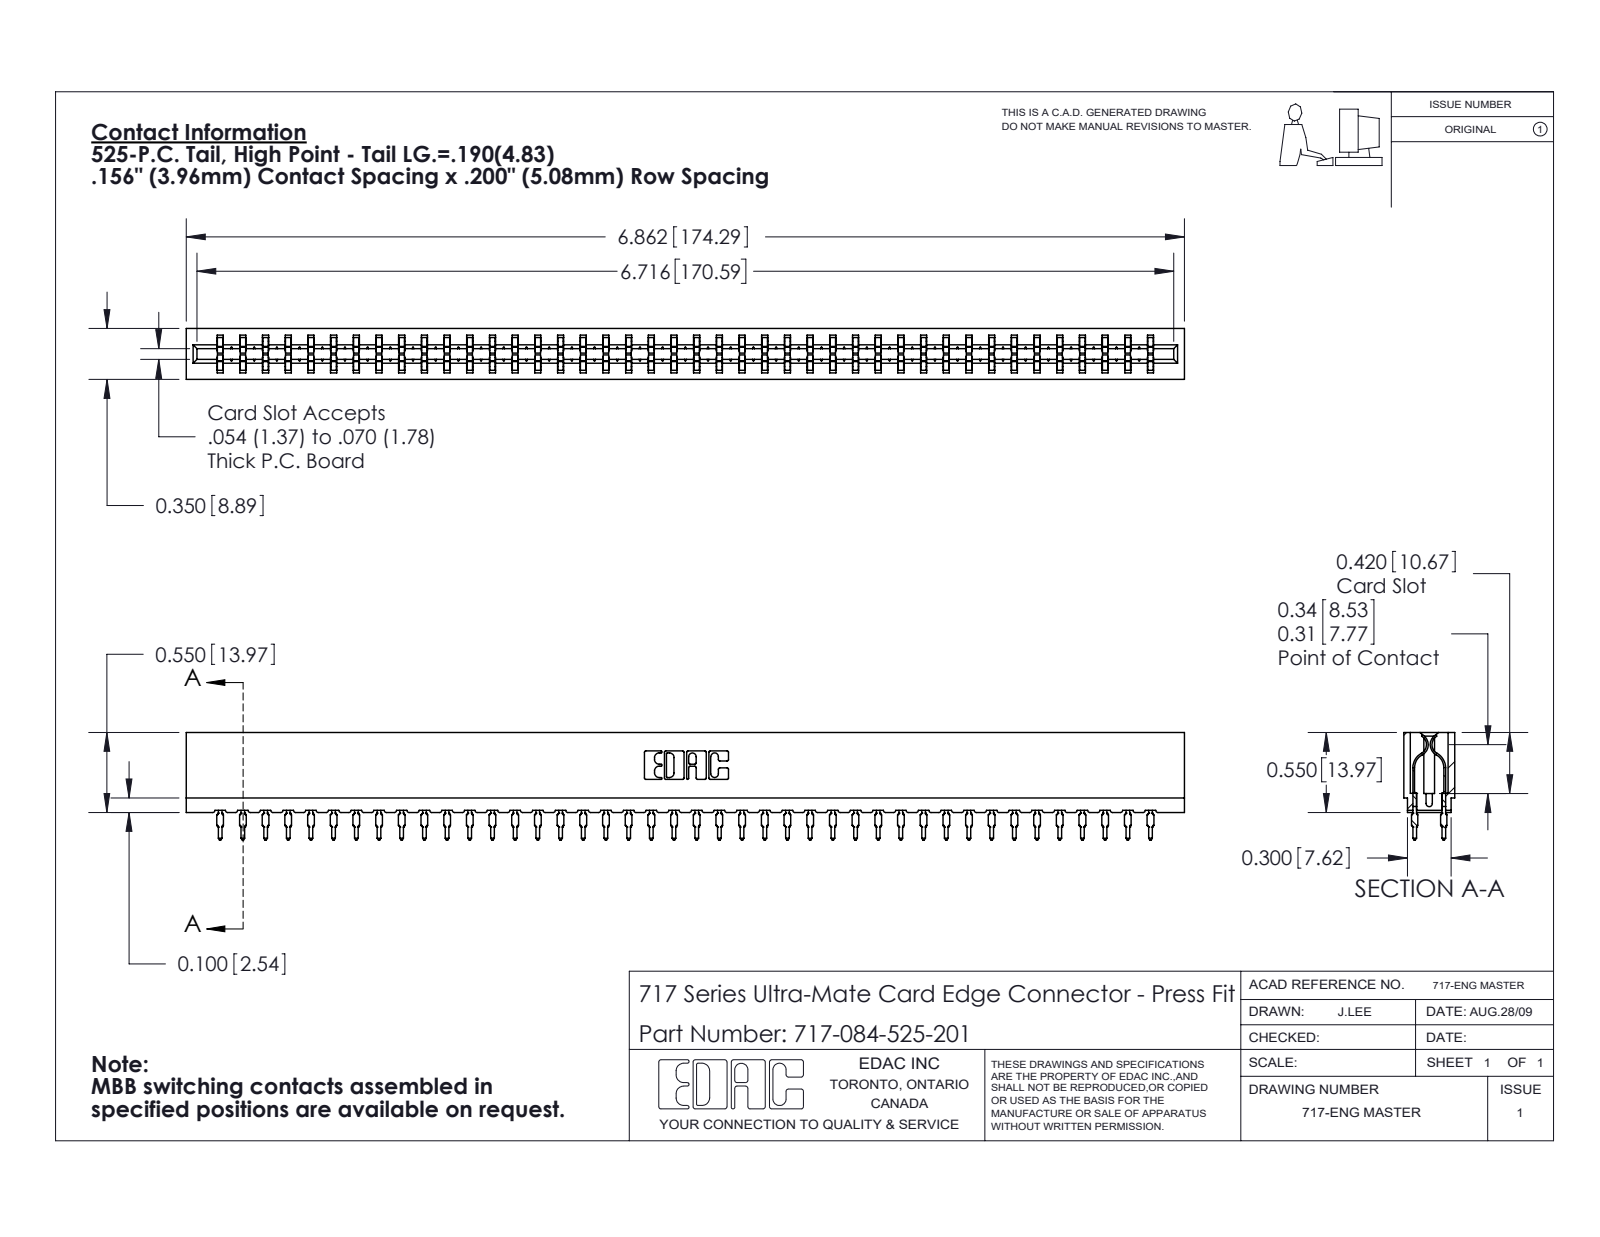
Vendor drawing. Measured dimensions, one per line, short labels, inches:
name: 717-084-525-201; 717 Part_Insulator Option - 06; 745-292-001_525
written by: SolidWorks 2020 (CONFIG_CONTROL_DESIGN)
unit: in
bodies: 85 solids, 7654 faces (3960 planar, 1510 cylindrical, 2184 other)
size: 6.862 × 0.739 × 0.35
volume: 0.92 in³; area: 35.61 in²
rounds: 168× R0.021, 84× R0.015, 22× R0.01, 8× R0.005, 8× R0.011, 6× R0.007, 6× R0.031, 3× R0.026
face distances: 0.212, 0.138, 0.35, 0.063, 0.287, 0.076, 0.149, 0.074, 0.045, 0.305
